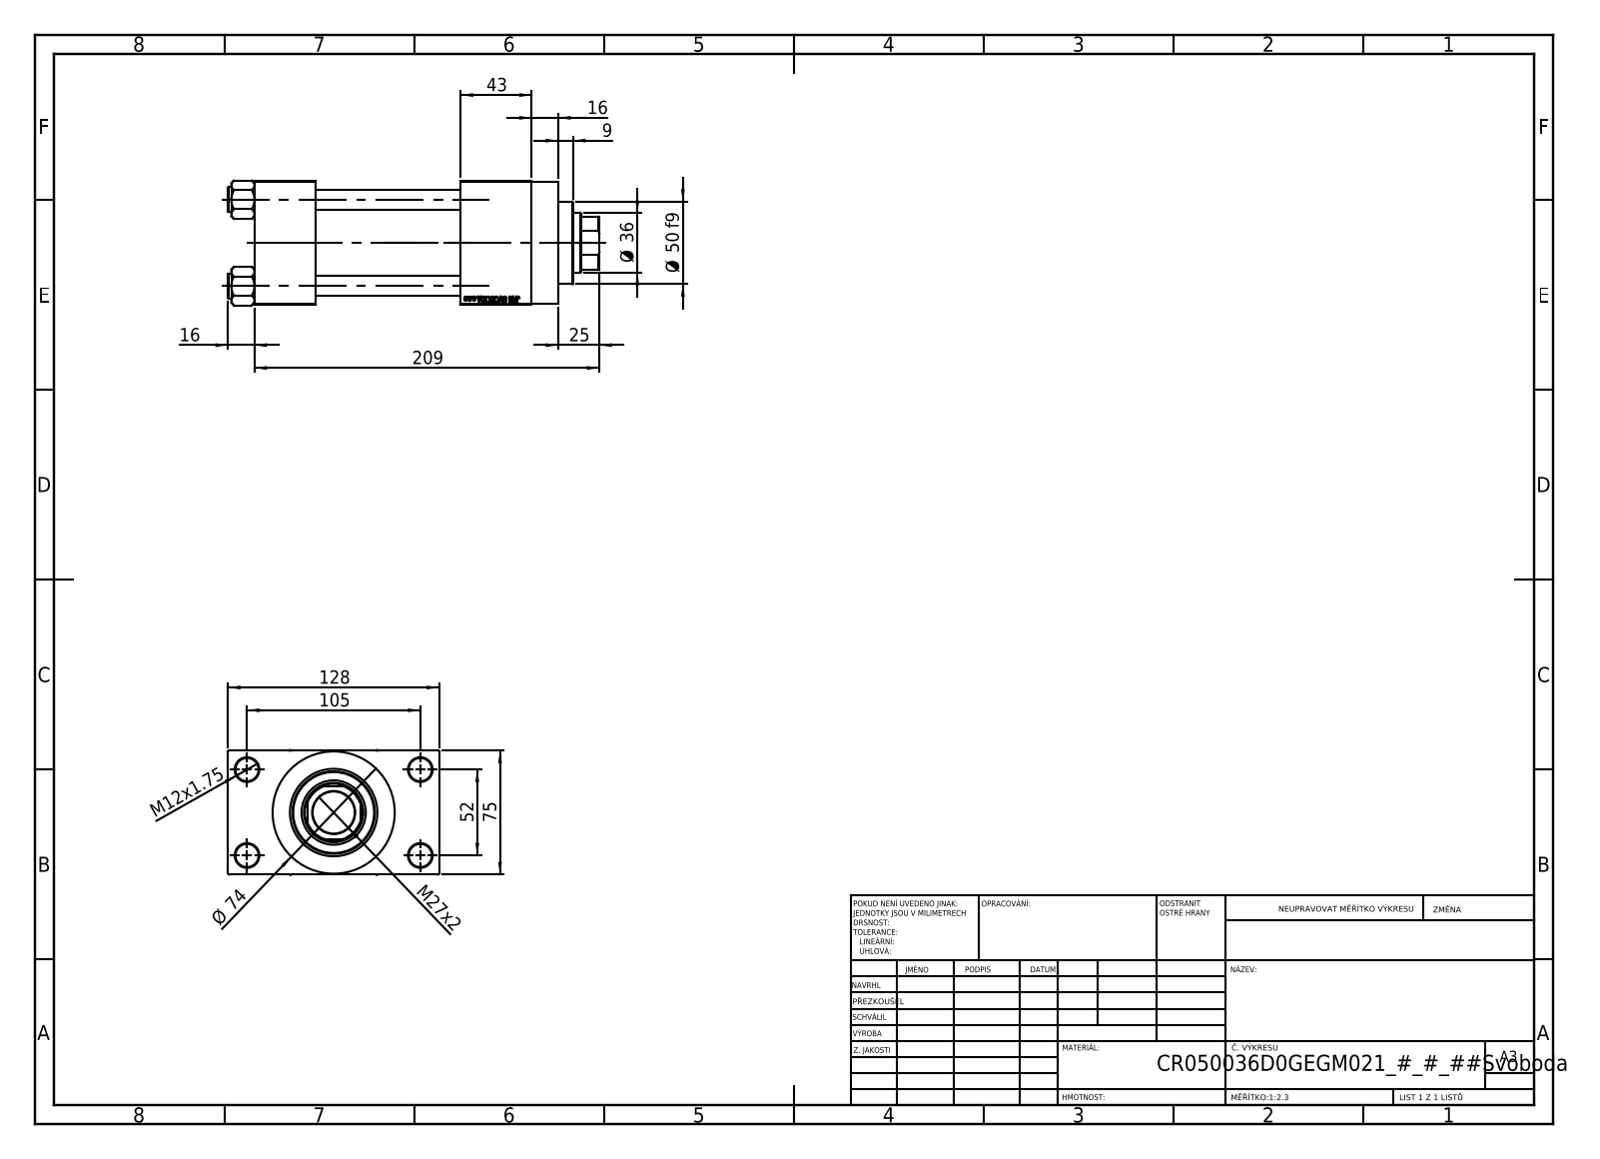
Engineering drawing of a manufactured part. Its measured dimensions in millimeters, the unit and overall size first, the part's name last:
Units: millimetres
Overall size (bounding box): 225 × 128 × 75.54
Round holes (diameter × count): ⌀12 ×4, ⌀14 ×4, ⌀7 ×2, ⌀20.96 ×2, ⌀30 ×2, ⌀25.5 ×1, ⌀36 ×1, ⌀39 ×1, ⌀41 ×1, ⌀53 ×1
Round bosses / shafts (diameter × count): ⌀15 ×4, ⌀74 ×1, ⌀56 ×1, ⌀50 ×1
Partial cylindrical surfaces — rounded edges, fillets, slot ends (radius × count): R17.5 ×1
Main face-to-face distances: 75, 88, 125, 37, 26.5, 101.5, 43, 168, 131, 16
Hole centre spacings: 26.35, 36.98, 52.3, 58.43, 58.59, 78.65, 94.37, 52
Volume: 885 459 mm³ · Surface area: 191 695 mm²
Bodies: 11 solids, 1104 faces (497 planar, 89 cylindrical, 518 other)
Part name (STEP PRODUCT): NUT_M5_D; V215CR_VCP_D; V215_VC_A; V215CR_D_Body (+1 more)
STEP written by: SolidWorks 2019 (CONFIG_CONTROL_DESIGN)
